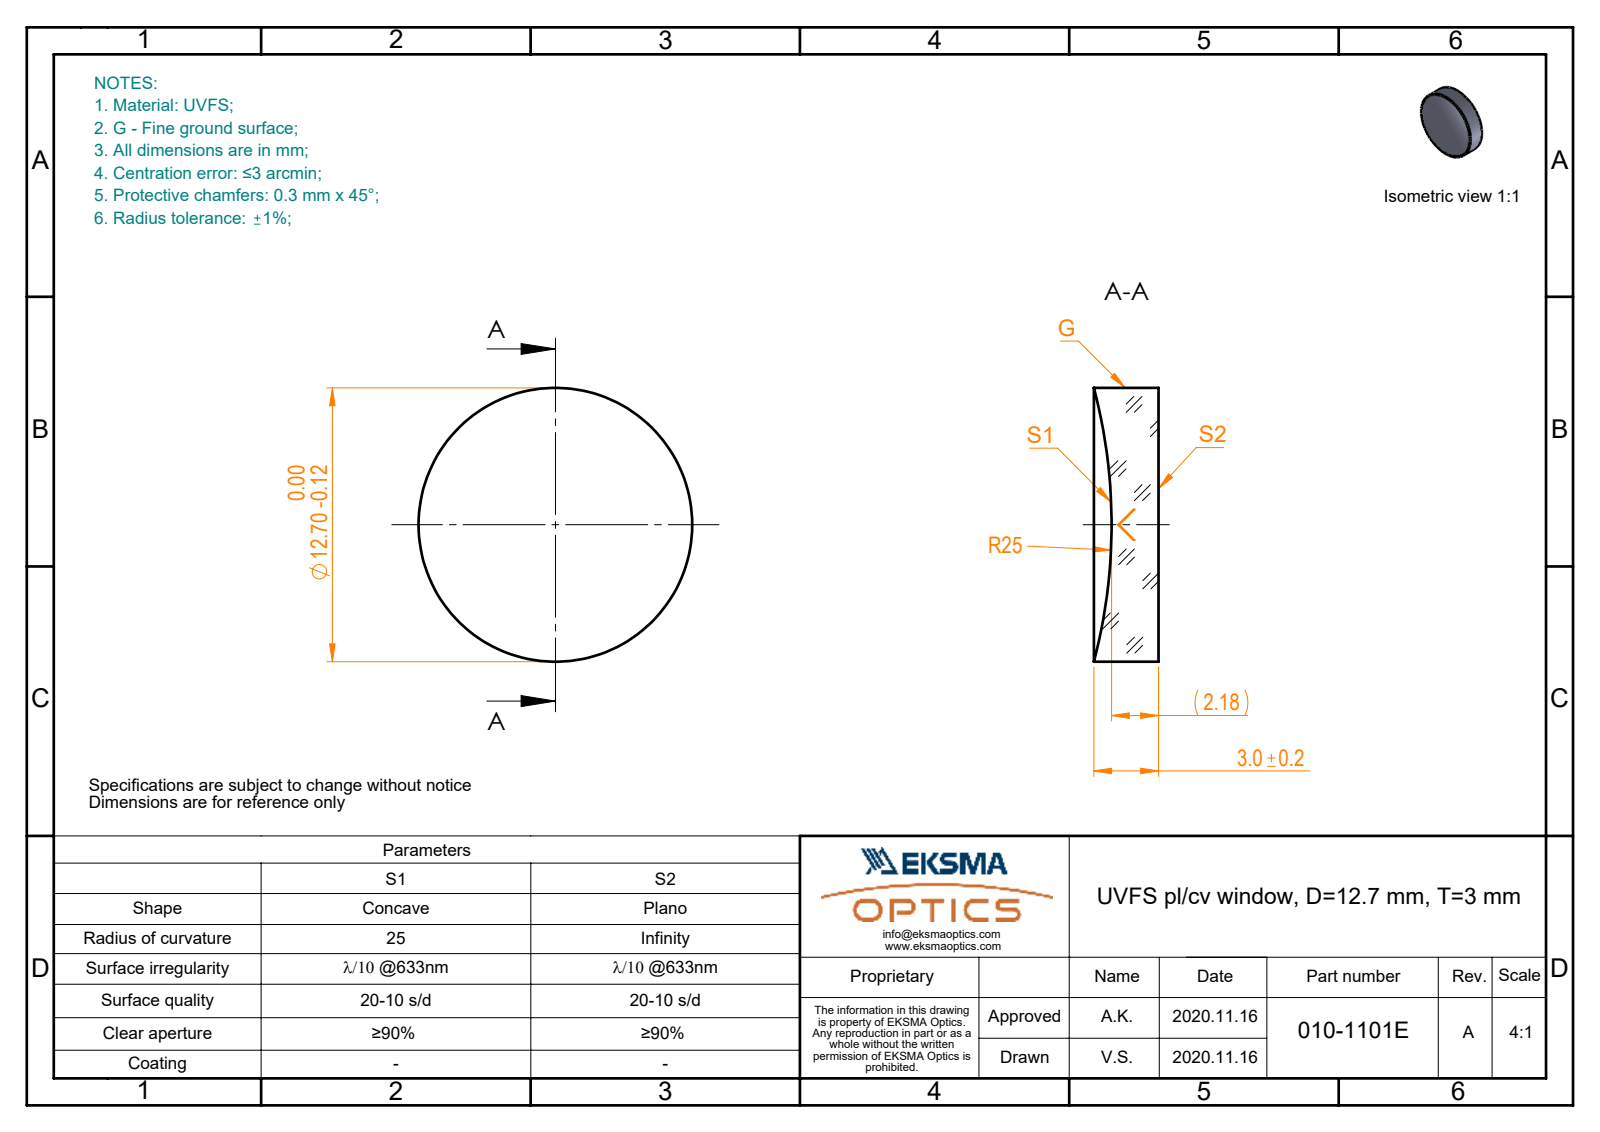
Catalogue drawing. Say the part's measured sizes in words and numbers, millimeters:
The part is named "010-1101E_UVFS_PCV_window". Its 3-D file was written by "SolidWorks 2019 (CONFIG_CONTROL_DESIGN)". It is 1 solid with 5 faces: 1 planar, 2 cylindrical and 2 other. Overall it measures 12.7 by 12.7 by 3 millimeters. Its volume is 328 cubic millimeters and its surface area 375 square millimeters. Round bosses or shafts: 1 of diameter 12.7.
